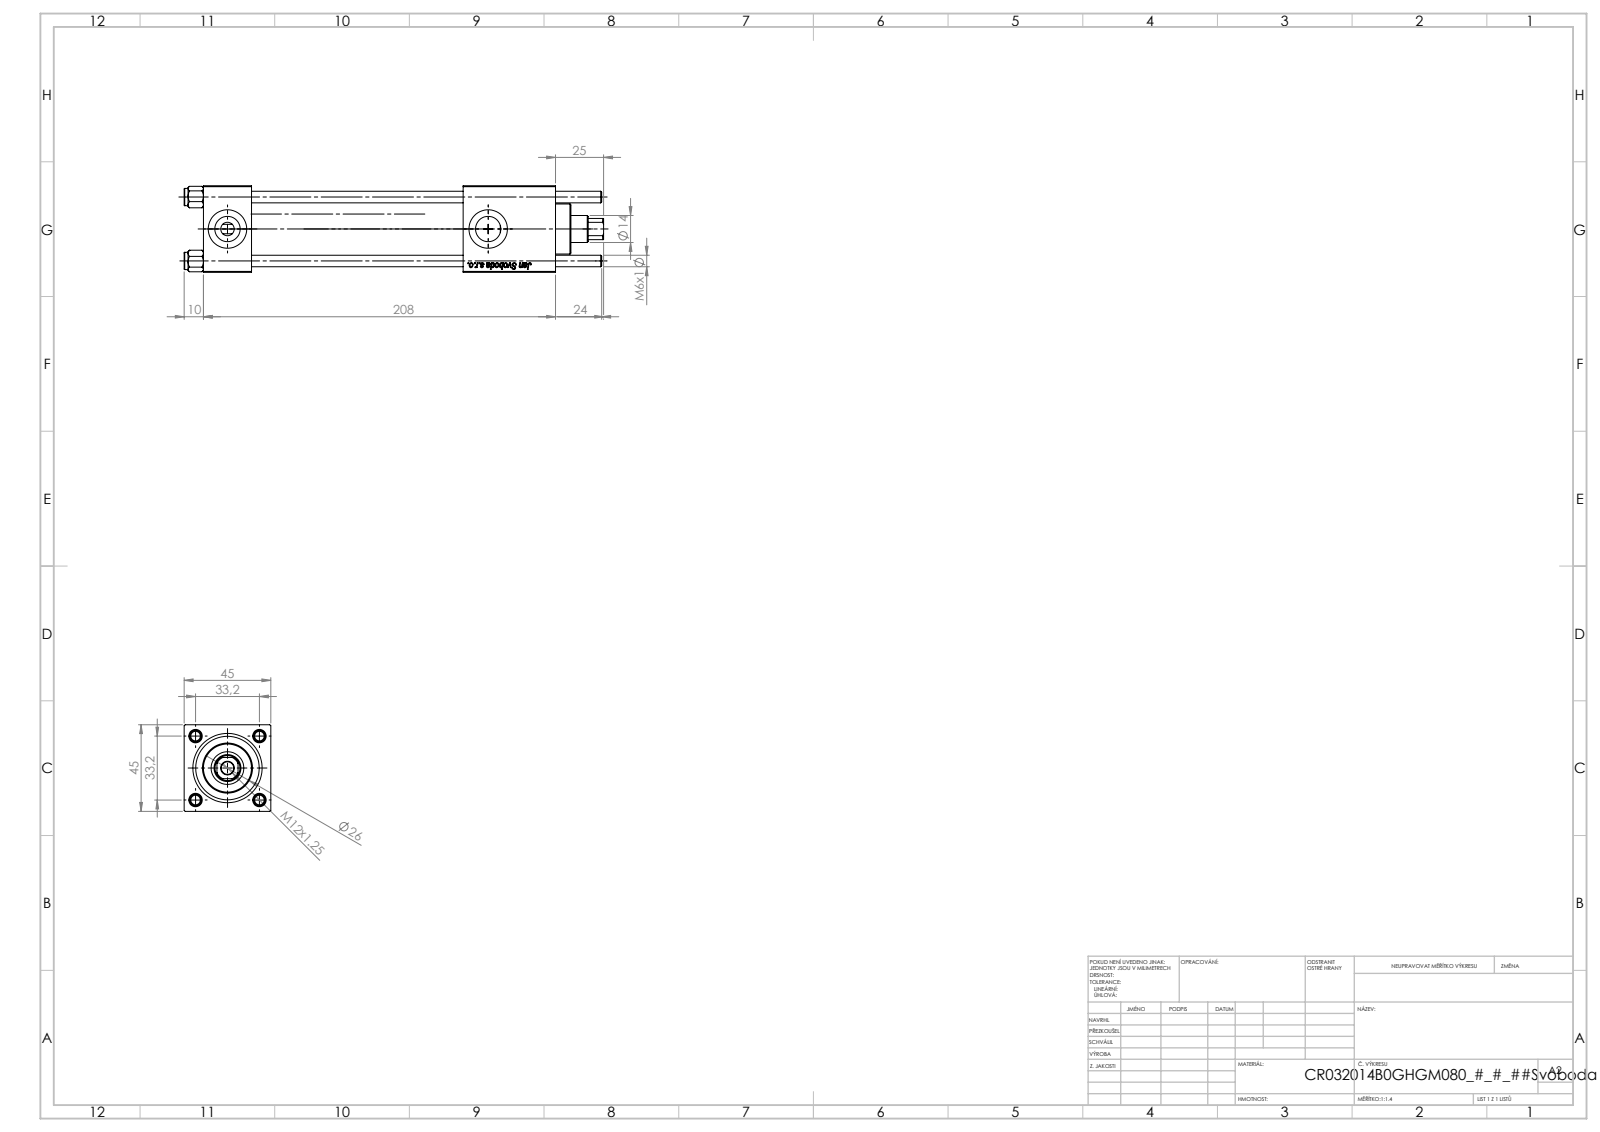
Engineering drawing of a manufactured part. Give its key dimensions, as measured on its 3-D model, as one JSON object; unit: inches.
{"part_name": "V215_VC_A; V215CR_B_TYCINKA; V215CR_VCP_B; NUT_M5_B (+1 more)", "step_written_by": "SolidWorks 2019 (CONFIG_CONTROL_DESIGN)", "units": "inches", "bodies": {"solids": 11, "faces": 1157, "planar": 431, "cylindrical": 78, "other": 648}, "overall_size": [8.583, 1.772, 1.772], "volume_in3": 14.29, "surface_area_in2": 144, "round_holes": [[0.236, 4], [0.276, 2], [0.518, 2], [0.787, 2], [0.256, 1], [0.551, 1], [0.669, 1], [0.945, 1], [1.26, 1], [1.299, 1]], "round_bosses_or_shafts": [[0.354, 4], [1.496, 1], [1.024, 1]], "partial_cylinders_radius": [[0.256, 1]], "face_to_face_distances": [1.772, 0.984, 7.205, 6.22, 5.315, 4.331, 1.89, 6.075, 5.091, 0.76], "hole_center_spacings": [0.924, 1.307, 1.848, 5.335]}
